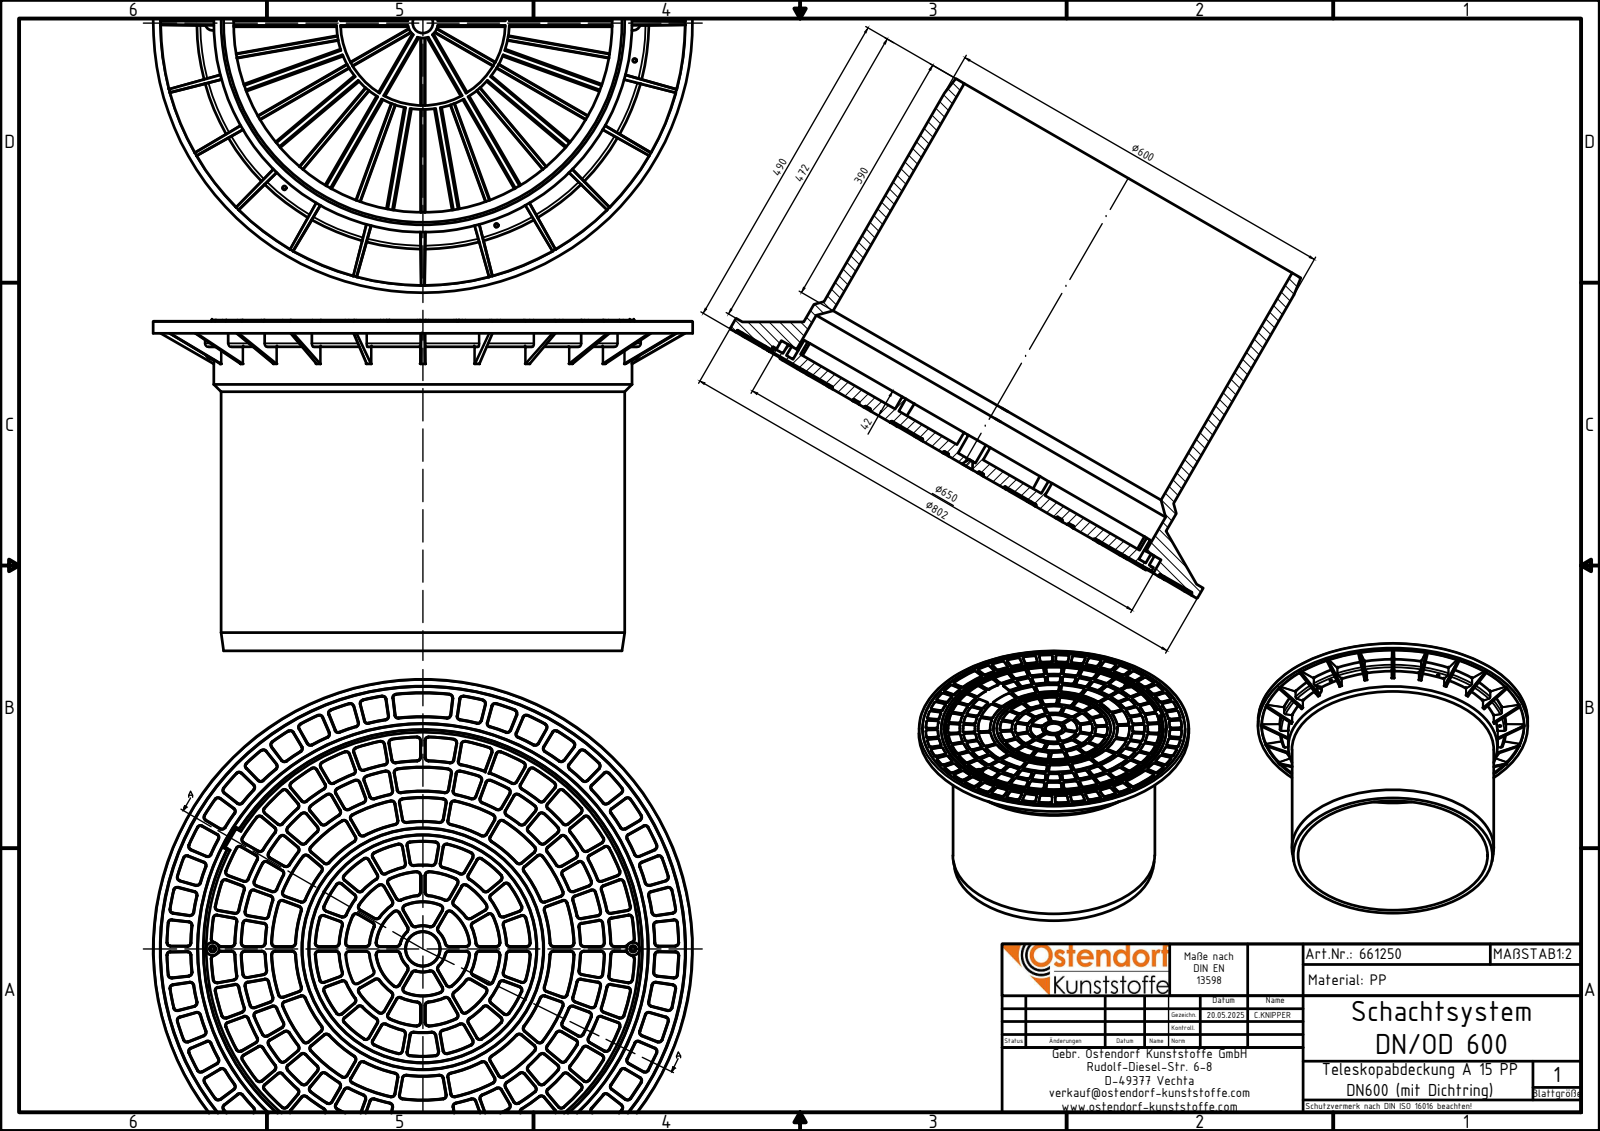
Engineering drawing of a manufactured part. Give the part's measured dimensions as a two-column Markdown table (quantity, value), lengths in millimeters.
| quantity | value |
| --- | --- |
| part name | 661250z; 661250_1; 661250_2 |
| STEP written by | Autodesk Inventor 2024 (AUTOMOTIVE_DESIGN) |
| units | millimeters |
| bodies | 2 solids, 5235 faces (865 planar, 2103 cylindrical, 2267 other) |
| overall size | 802 × 802 × 491.5 |
| volume | 23 430 000 mm³ |
| surface area | 3 618 000 mm² |
| round holes (diameter × count) | 5.5 × 6, 6.65 × 2, 9.5 × 2, 19.5 × 2, 30 × 1, 245 × 1, 339 × 1, 563 × 1, 582 × 1, 600 × 1, 617 × 1, 780 × 1 |
| round bosses / shafts (diameter × count) | 802 × 1, 672 × 1, 670 × 1, 644 × 1, 629 × 1, 622 × 1, 594 × 1, 359 × 1 |
| partial cylindrical surfaces (radius × count) | 5 × 678, 1 × 519, 0.8 × 260, 4 × 12, 11 × 2, 11.5 × 2, 22.5 × 1, 34.5 × 1 |
| main face-to-face distances | 9.5, 1.5, 11, 4, 13.5, 15, 12, 5.5, 24.5, 8 |
| hole center spacings | 320, 554.25, 55.63, 267.39, 312.5, 362.84, 518.13, 554.26 |
